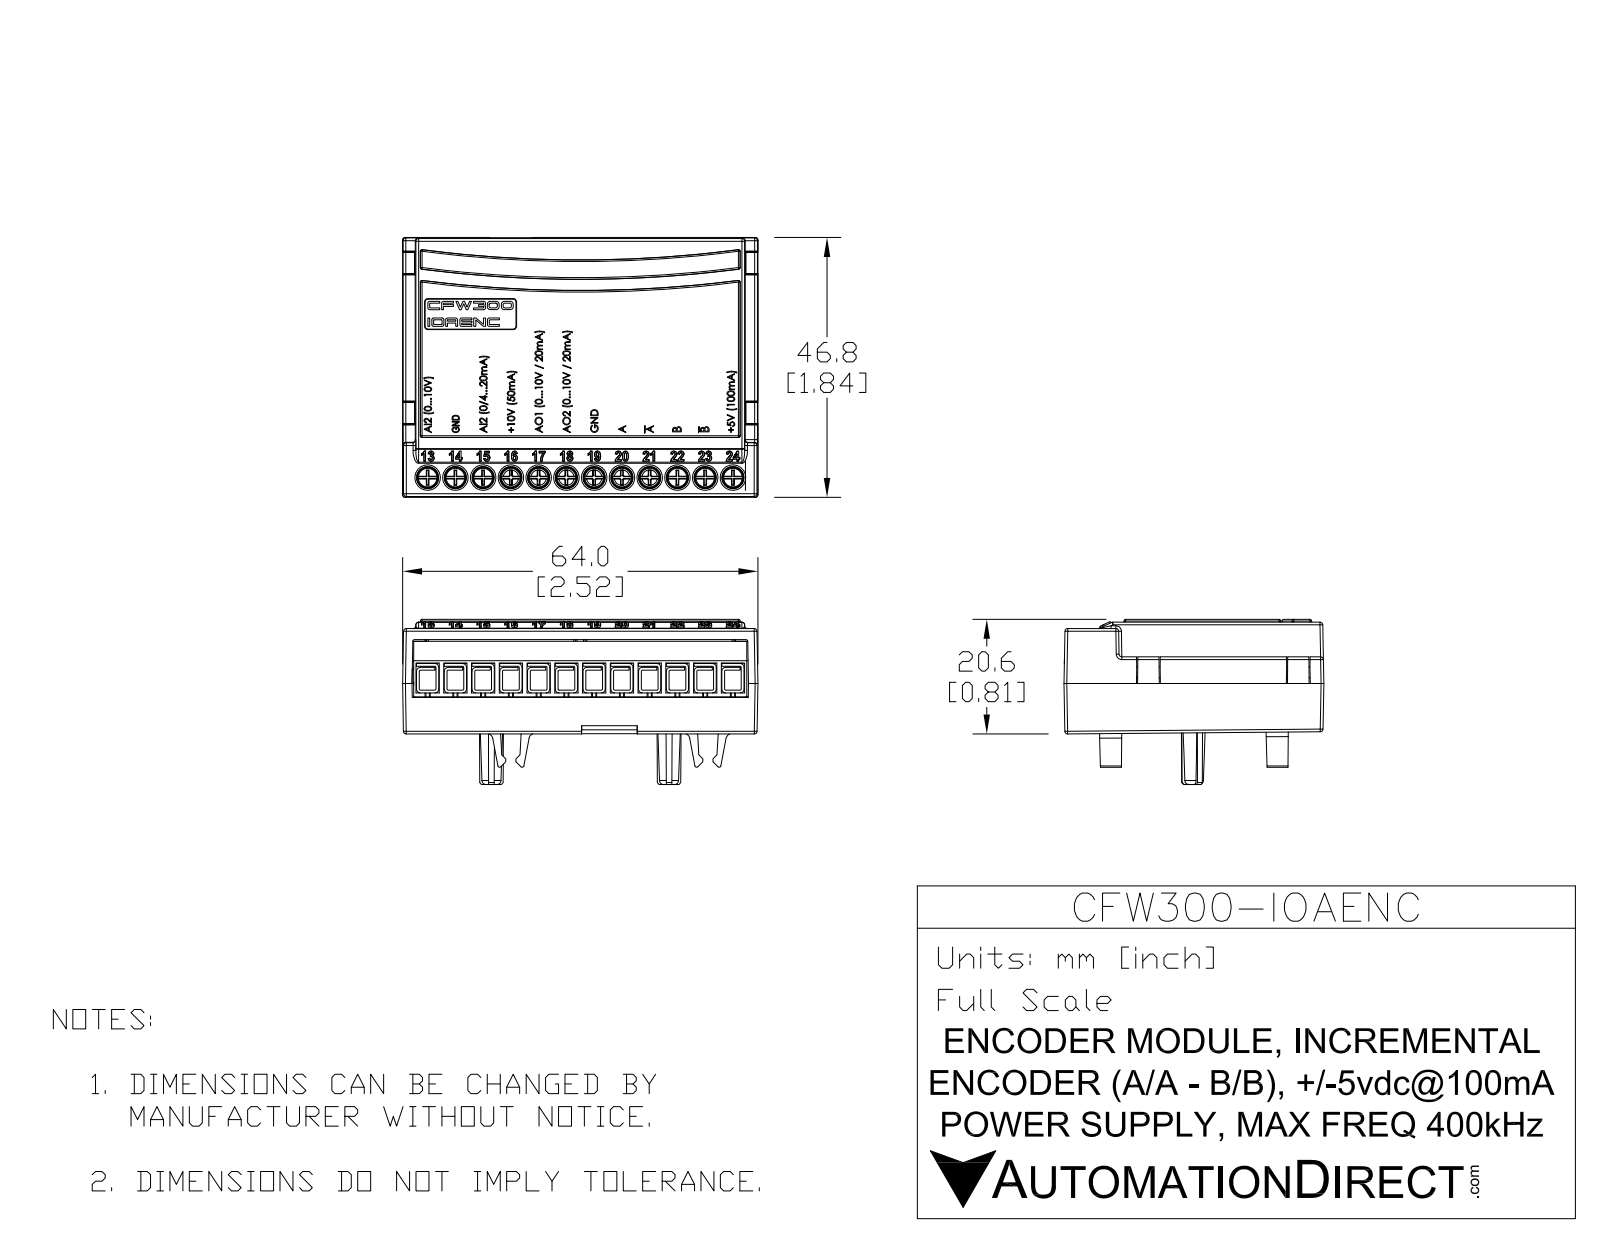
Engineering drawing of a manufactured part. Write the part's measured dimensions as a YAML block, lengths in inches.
part_name: "CFW300-IOAENC"
step_written_by: "SolidWorks 2017 (AUTOMOTIVE_DESIGN)"
units: inches
bodies: {solids: 1, faces: 1994, planar: 1207, cylindrical: 195, other: 592}
overall_size: [2.52, 1.854, 0.813]
volume: 3.531
surface_area: 22.74
round_holes:
  - {diameter: 0.18, count: 12}
round_bosses_or_shafts:
  - {diameter: 0.153, count: 12}
partial_cylinders:
  - {radius: 0.008, count: 48}
  - {radius: 0.028, count: 48}
  - {radius: 0.039, count: 16}
  - {radius: 0.02, count: 4}
  - {radius: 0.024, count: 4}
  - {radius: 0.01, count: 3}
face_to_face_distances: [0.812, 1.849, 2.52, 0.02, 0.028, 0.189, 0.091, 2.429, 0.25, 1.599]
hole_center_spacings: [0.197, 0.394, 0.591, 0.787, 0.984, 1.181, 1.378, 1.575]
